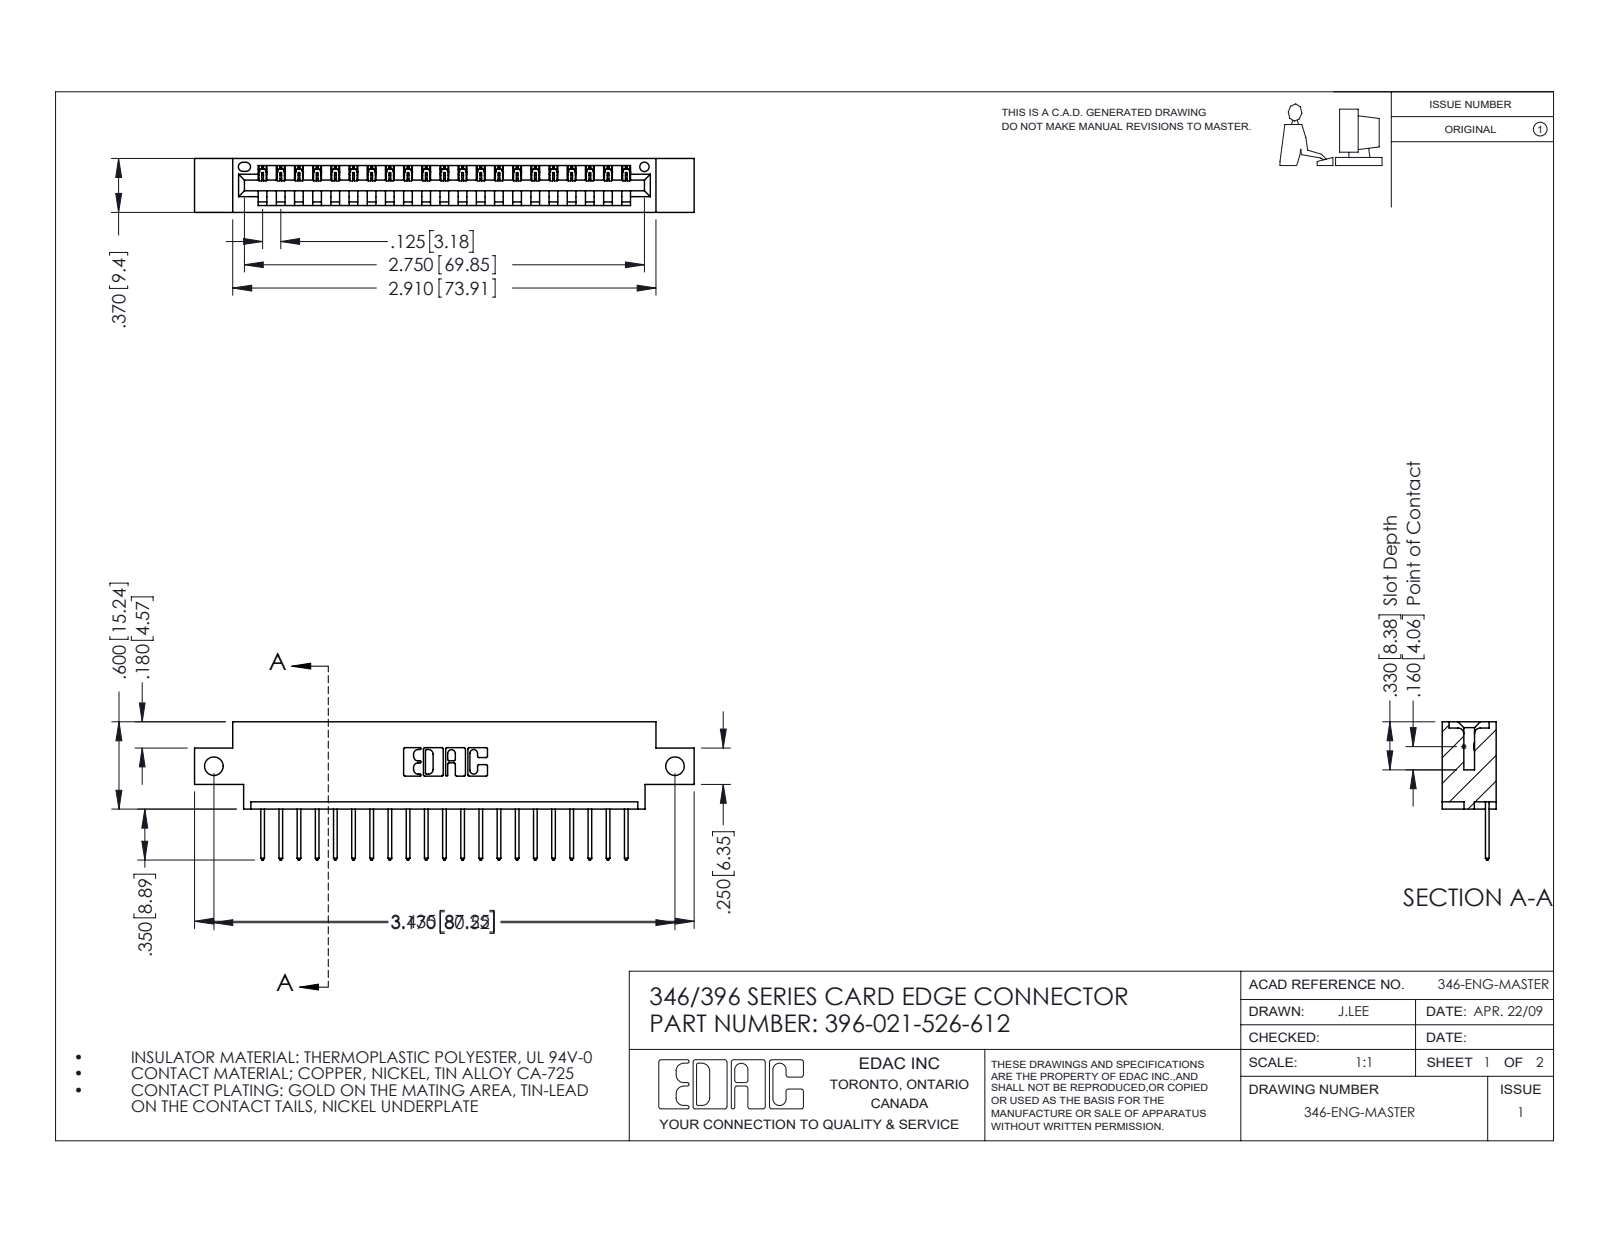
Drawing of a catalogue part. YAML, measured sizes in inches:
part_name: "396-021-526-612; 345-292-001_345-293-126; 346 Part_0.170 Offset - Side Mount"
step_written_by: "SolidWorks 2016 (CONFIG_CONTROL_DESIGN)"
units: inches
bodies: {solids: 22, faces: 1344, planar: 920, cylindrical: 424, other: 0}
overall_size: [3.435, 0.95, 0.37]
volume: 0.485
surface_area: 15.04
round_holes:
  - {diameter: 0.128, count: 2}
  - {diameter: 0.064, count: 1}
partial_cylinders:
  - {radius: 0.006, count: 42}
  - {radius: 0.01, count: 42}
  - {radius: 0.01, count: 22}
  - {radius: 0.007, count: 6}
  - {radius: 0.031, count: 6}
  - {radius: 0.026, count: 3}
  - {radius: 0.031, count: 2}
  - {radius: 0.04, count: 2}
face_to_face_distances: [0.048, 0.322, 0.37, 0.25, 0.072, 0.298, 0.025, 0.148, 0.222, 0.1]
hole_center_spacings: [3.17]
